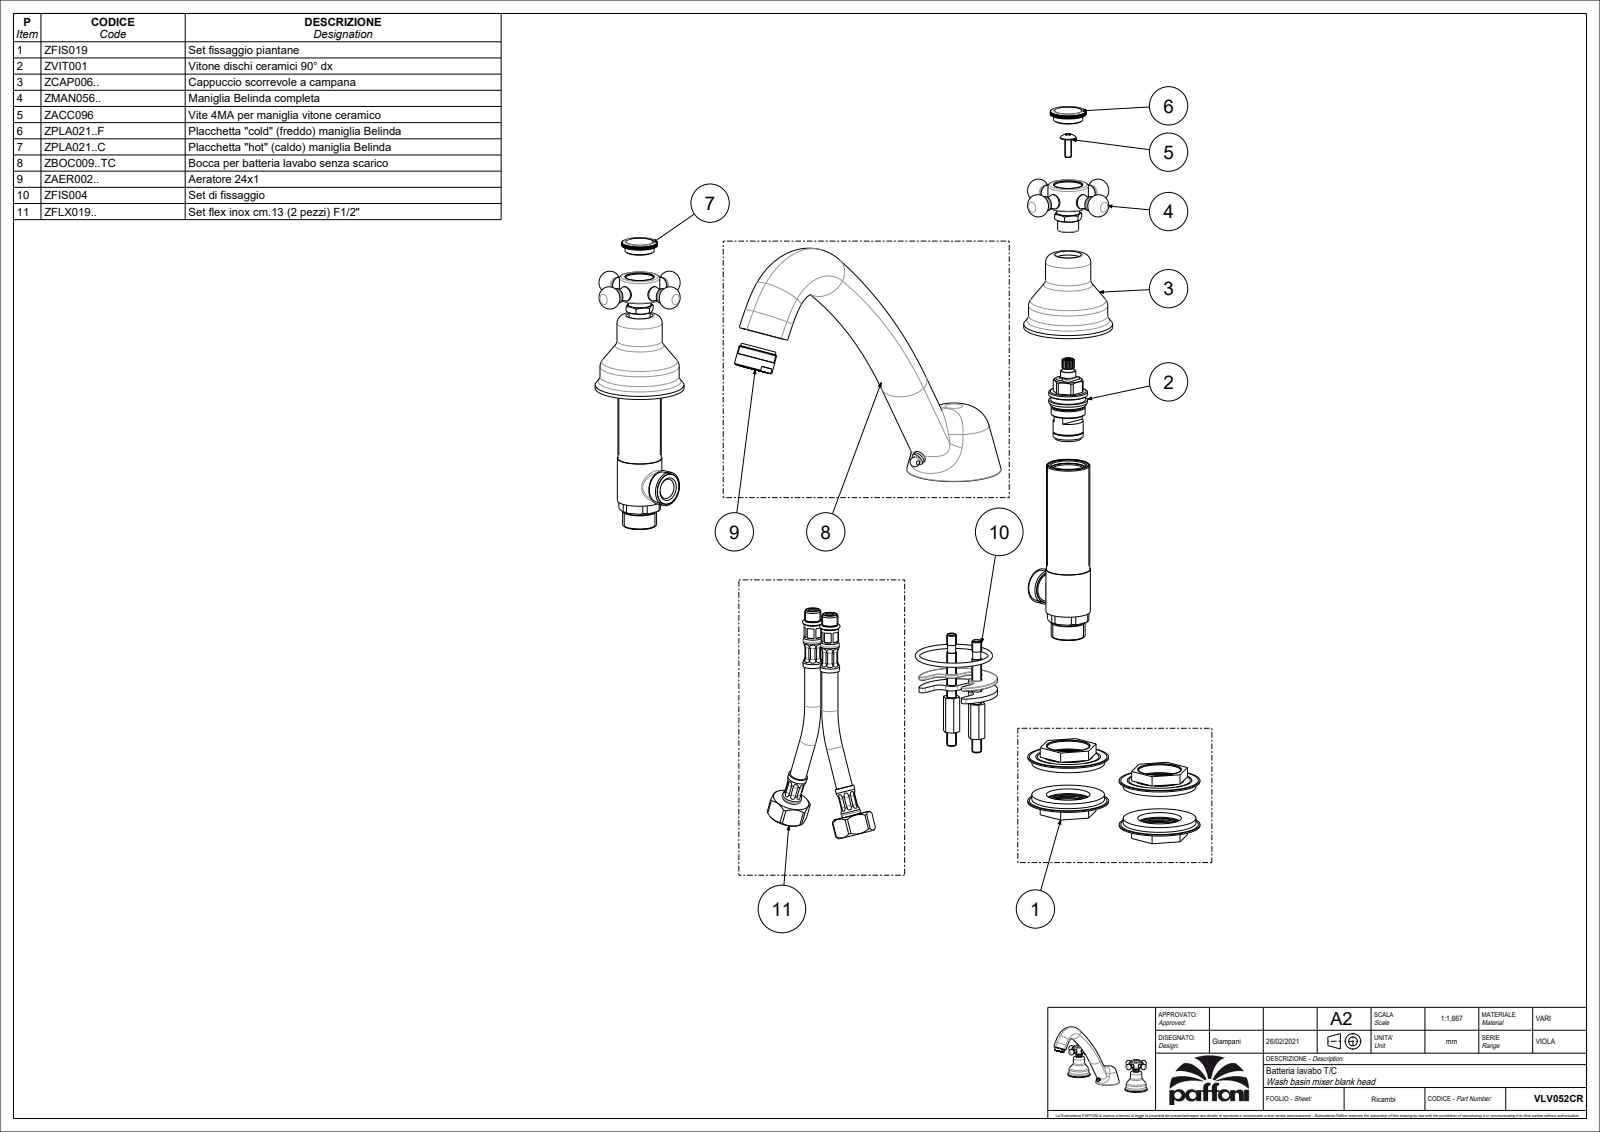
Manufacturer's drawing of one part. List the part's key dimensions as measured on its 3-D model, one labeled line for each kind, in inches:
Part name (STEP PRODUCT): VLV052CR
STEP written by: CREO PARAMETRIC BY PTC INC, 2020044 (CONFIG_CONTROL_DESIGN)
Units: inches
Bodies: 3 solids, 1106 faces (470 planar, 335 cylindrical, 301 other)
Overall size (bounding box): 10.396 × 8.391 × 6.513
Volume: 15.51 in³ · Surface area: 132.1 in²
Round holes (diameter × count): ⌀0.217 ×2, ⌀0.354 ×2, ⌀0.433 ×2, ⌀0.63 ×1, ⌀0.787 ×1, ⌀0.827 ×1, ⌀0.906 ×1, ⌀1.89 ×1
Round bosses / shafts (diameter × count): ⌀0.354 ×3, ⌀0.276 ×3, ⌀2.165 ×2, ⌀1.929 ×2, ⌀1.102 ×2, ⌀0.984 ×2, ⌀0.551 ×2, ⌀0.512 ×2
Partial cylindrical surfaces — rounded edges, fillets, slot ends (radius × count): R0.039 ×8, R0.098 ×8, R0.031 ×5, R0.197 ×2, R0.433 ×2, R0.073 ×1, R0.736 ×1, R0.787 ×1
Main face-to-face distances: 0.354, 1.898, 0.118, 2.252, 0.079, 0.276, 2.173, 0.305, 0.236, 0.303
Hole centre spacings: 0.378, 0.559, 0.606, 0.938, 0.591, 0.866
